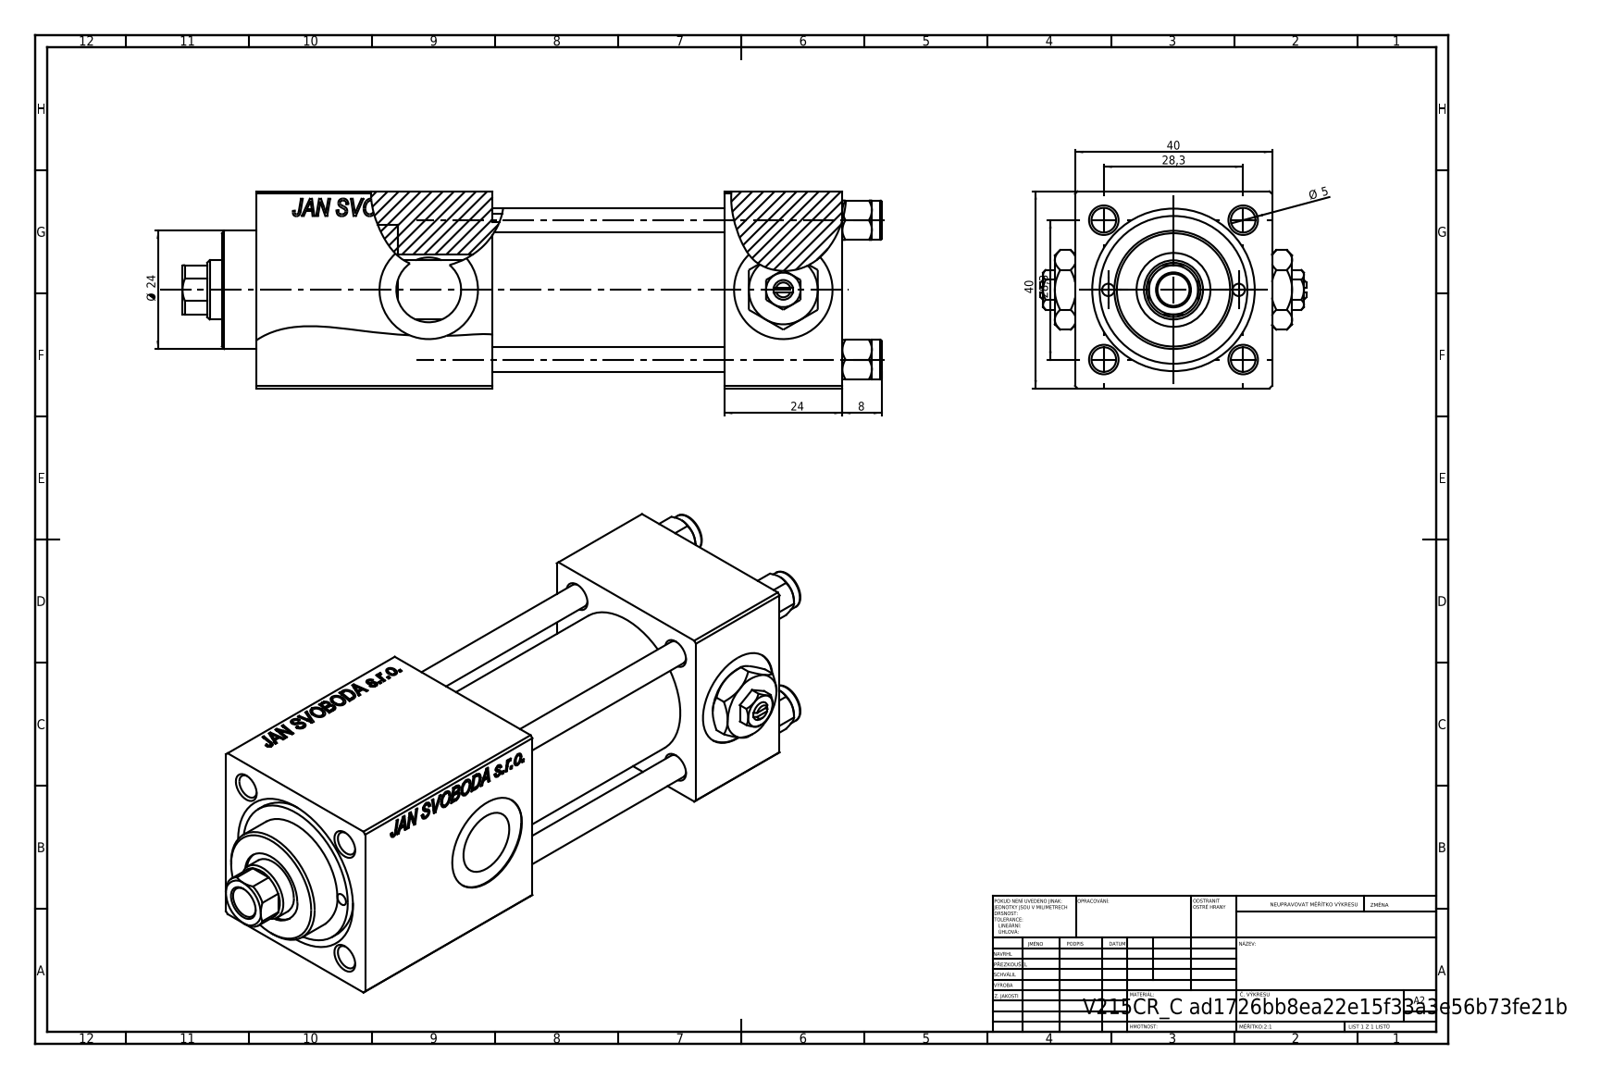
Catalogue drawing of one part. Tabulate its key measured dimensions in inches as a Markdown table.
| quantity | value |
| --- | --- |
| part name | Zatka_pro_OIL_PORT; V215CR_C_Body; V215CR_VCP_C; V215_VC_A (+2 more) |
| STEP written by | SolidWorks 2019 (CONFIG_CONTROL_DESIGN) |
| units | inches |
| bodies | 13 solids, 1254 faces (574 planar, 102 cylindrical, 578 other) |
| overall size | 5.591 × 2.126 × 1.575 |
| volume | 8.6 in³ |
| surface area | 87.25 in² |
| round holes (diameter × count) | 0.197 × 4, 0.787 × 3, 0.098 × 2, 0.276 × 2, 0.518 × 2, 0.256 × 1, 0.472 × 1, 0.591 × 1, 0.984 × 1, 1.181 × 1 |
| round bosses / shafts (diameter × count) | 0.315 × 4, 1.22 × 1, 0.945 × 1 |
| partial cylindrical surfaces (radius × count) | 0.217 × 1 |
| main face-to-face distances | 1.575, 0.945, 1.567, 3.555, 2.61, 1.85, 1.89, 2.795, 0.76, 3.74 |
| hole center spacings | 0.558, 0.788, 1.114, 1.214, 0.522, 1.576, 1.043, 2.835 |
